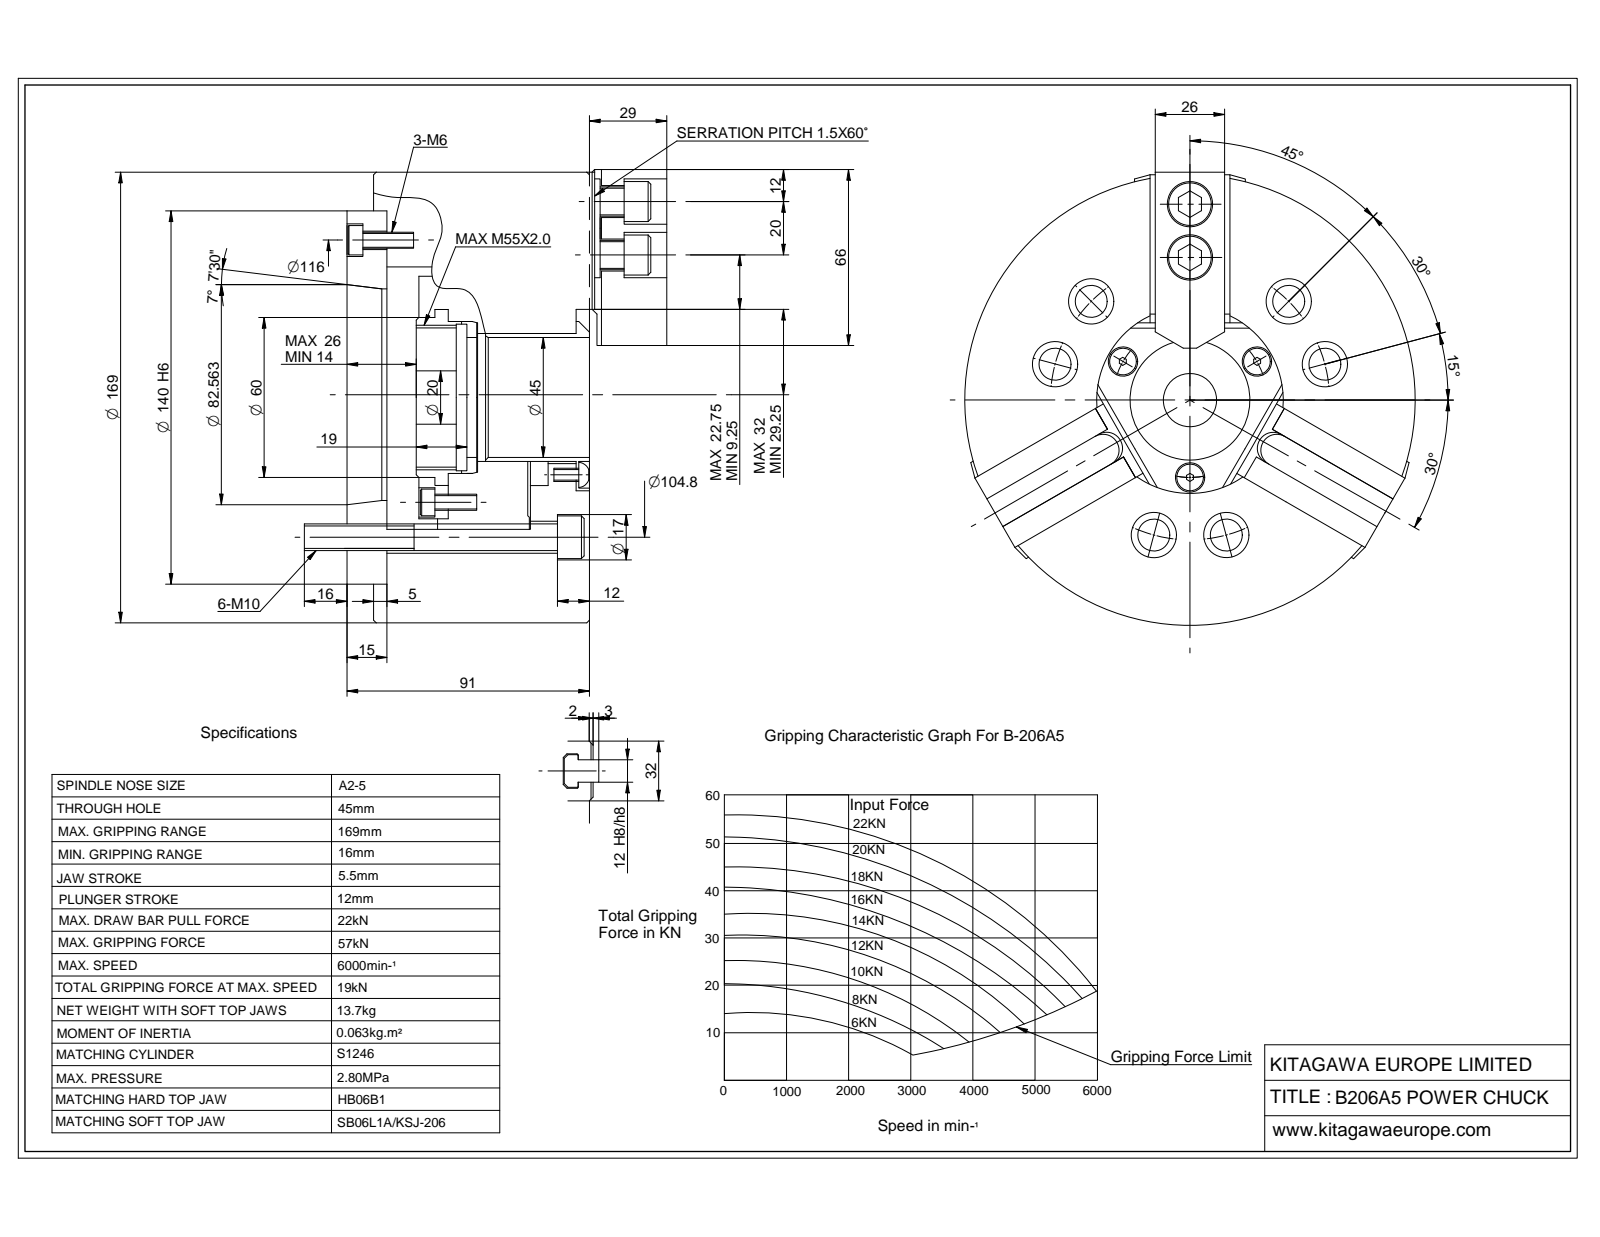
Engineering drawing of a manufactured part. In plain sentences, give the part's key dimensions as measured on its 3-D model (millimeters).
The part is named "b206a5". Its 3-D file was written by "ST-DEVELOPER v16.7 (AUTOMOTIVE_DESIGN)". It is 1 solid with 2054 faces: 1494 planar, 250 cylindrical and 310 other. Overall it measures 169 by 169 by 93.3 millimeters. Its volume is 1 512 000 cubic millimeters and its surface area 223 632 square millimeters. Round holes: 12 of diameter 5, 11 of diameter 11, 9 of diameter 6.6, 6 of diameter 12, 6 of diameter 17, 3 of diameter 1, 3 of diameter 4.2, 3 of diameter 5.5, 3 of diameter 10, 3 of diameter 10.3, 3 of diameter 13.5, 3 of diameter 16.28. Round bosses or shafts: 6 of diameter 10, 6 of diameter 6, 1 of diameter 169, 1 of diameter 140, 1 of diameter 98, 1 of diameter 91, 1 of diameter 64.5, 1 of diameter 60. Partial cylindrical surfaces (rounded edges, fillets, slot ends): 12 of radius 0.8, 9 of radius 4, 6 of radius 0.6, 6 of radius 0.81, 4 of radius 24.5, 3 of radius 5, 3 of radius 5.2, 3 of radius 6. The main face-to-face distances are 10, 5, 91, 12.5, 81, 17.5, 27.5, 15, 76, 0.5. The hole center spacings are 52.39, 90.74, 13.39, 26.95, 27.12, 29.08, 39, 47.14.
